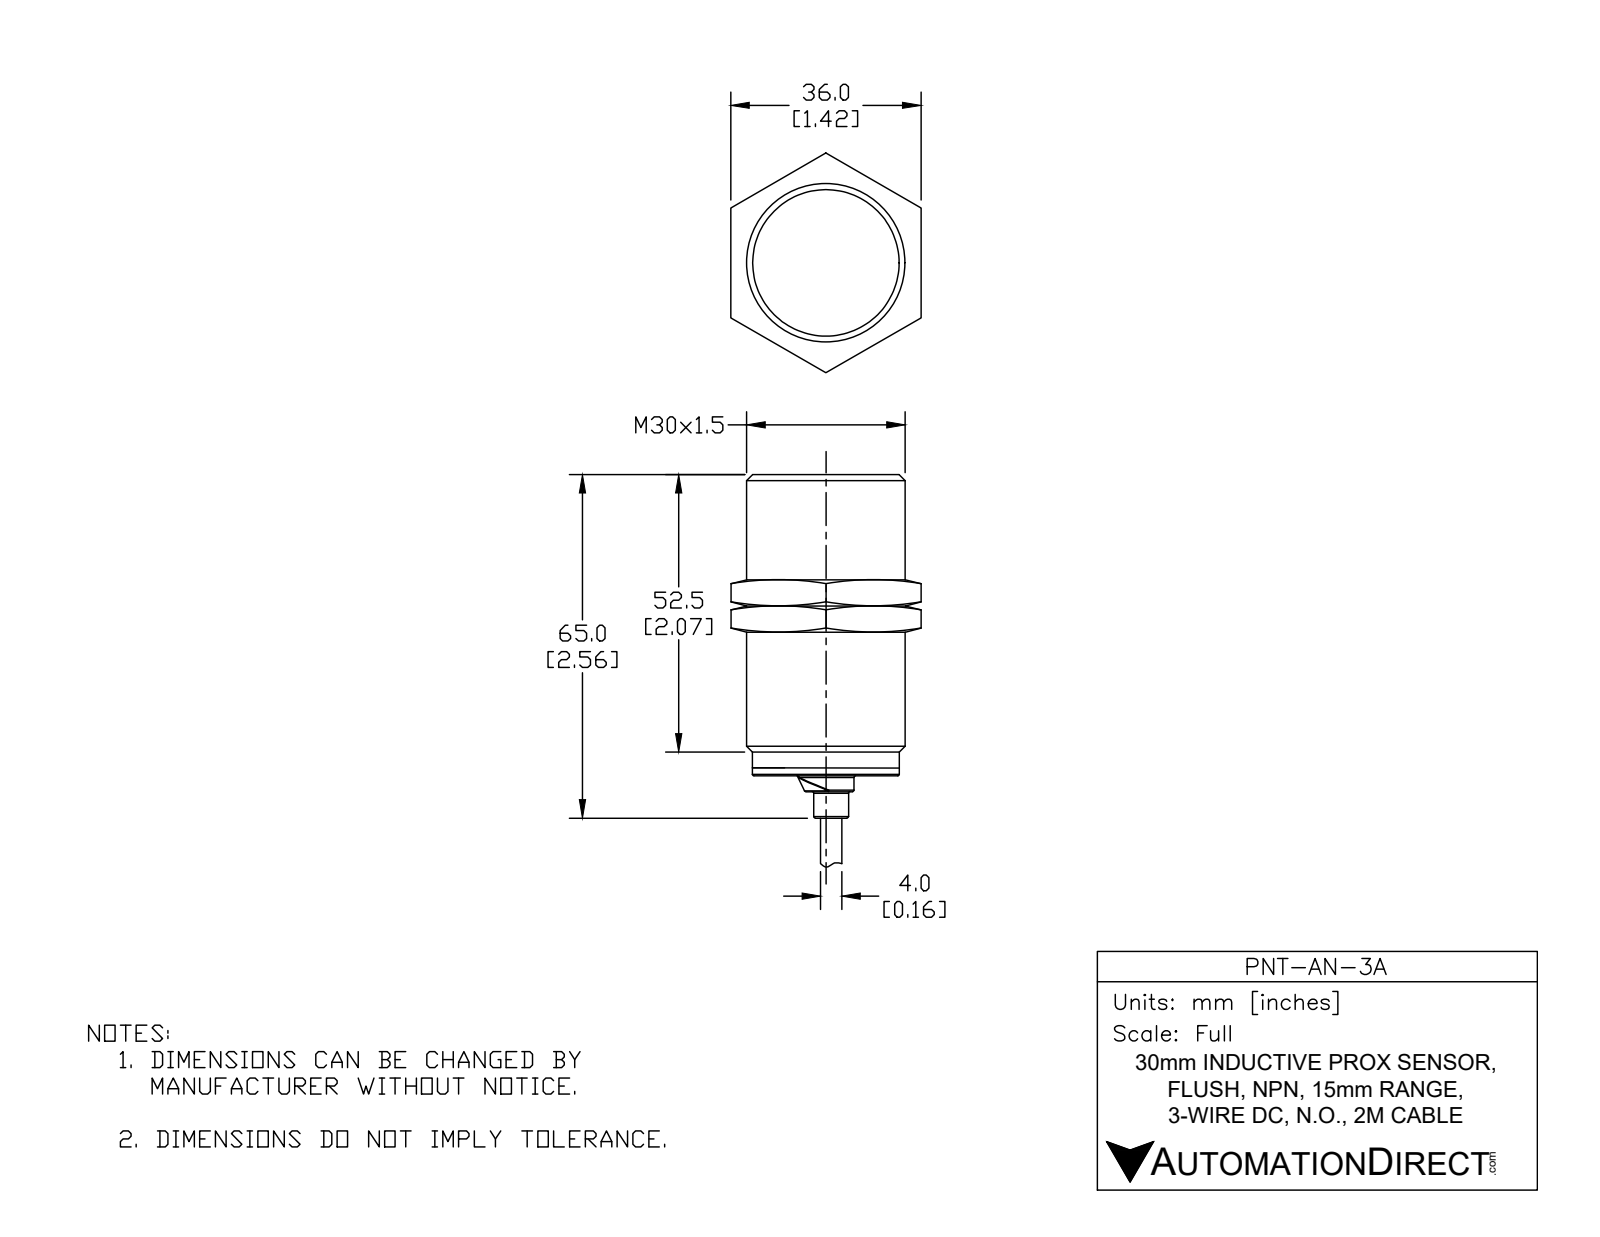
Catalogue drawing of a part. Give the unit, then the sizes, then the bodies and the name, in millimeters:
Units: millimetres
Overall size (bounding box): 115.8 × 30 × 30
Round holes (diameter × count): ⌀4.1 ×1
Round bosses / shafts (diameter × count): ⌀1.2 ×6, ⌀30 ×1, ⌀27.8 ×1, ⌀27.8 ×1, ⌀10.6 ×1, ⌀6.6 ×1, ⌀4 ×1
Partial cylindrical surfaces — rounded edges, fillets, slot ends (radius × count): R2 ×1
Main face-to-face distances: 57, 60, 3, 57.9, 65, 8, 5, 115.8, 58.8, 55.8
Volume: 40 750 mm³ · Surface area: 7 677 mm²
Bodies: 1 solid, 74 faces (14 planar, 30 cylindrical, 30 other)
Part name (STEP PRODUCT): PNT-AN-3A
STEP written by: SolidWorks 2017 (AUTOMOTIVE_DESIGN)
